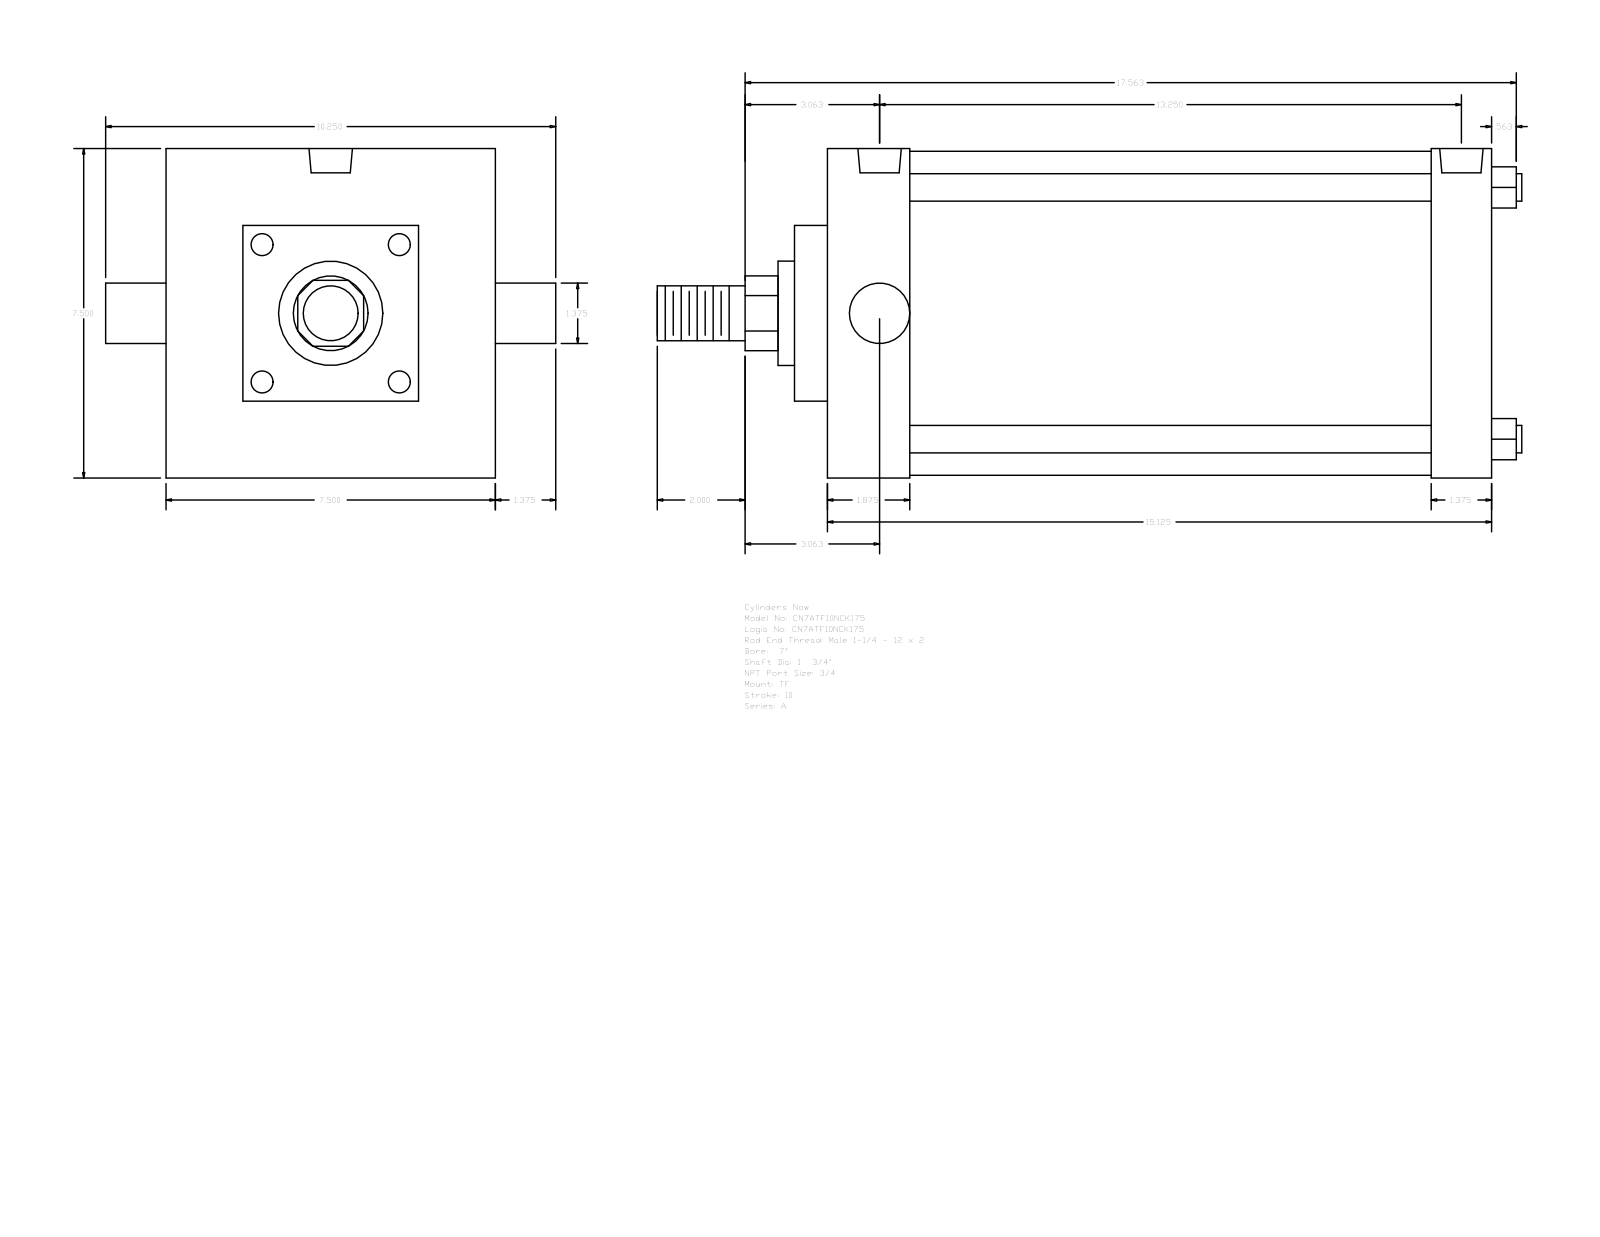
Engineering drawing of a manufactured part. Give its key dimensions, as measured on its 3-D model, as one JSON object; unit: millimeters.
{"part_name": "A_TF__0700_1.75", "step_written_by": "GSSL Pune (CONFIG_CONTROL_DESIGN)", "units": "millimeters", "bodies": {"solids": 0, "faces": 89, "planar": 65, "cylindrical": 24, "other": 0}, "overall_size": [500.06, 260.35, 190.5], "round_holes": [[15.08, 3], [25.12, 2]], "round_bosses_or_shafts": [[15.88, 4], [187.32, 1], [60.33, 1], [44.45, 1], [34.92, 1], [31.75, 1]], "partial_cylinders_radius": [[21.63, 1]], "face_to_face_distances": [190.5, 384.18, 146.05, 19.05, 47.63, 336.55, 349.26, 301.63, 34.92, 44.45], "hole_center_spacings": [5.56, 330.99, 325.43, 336.55]}
